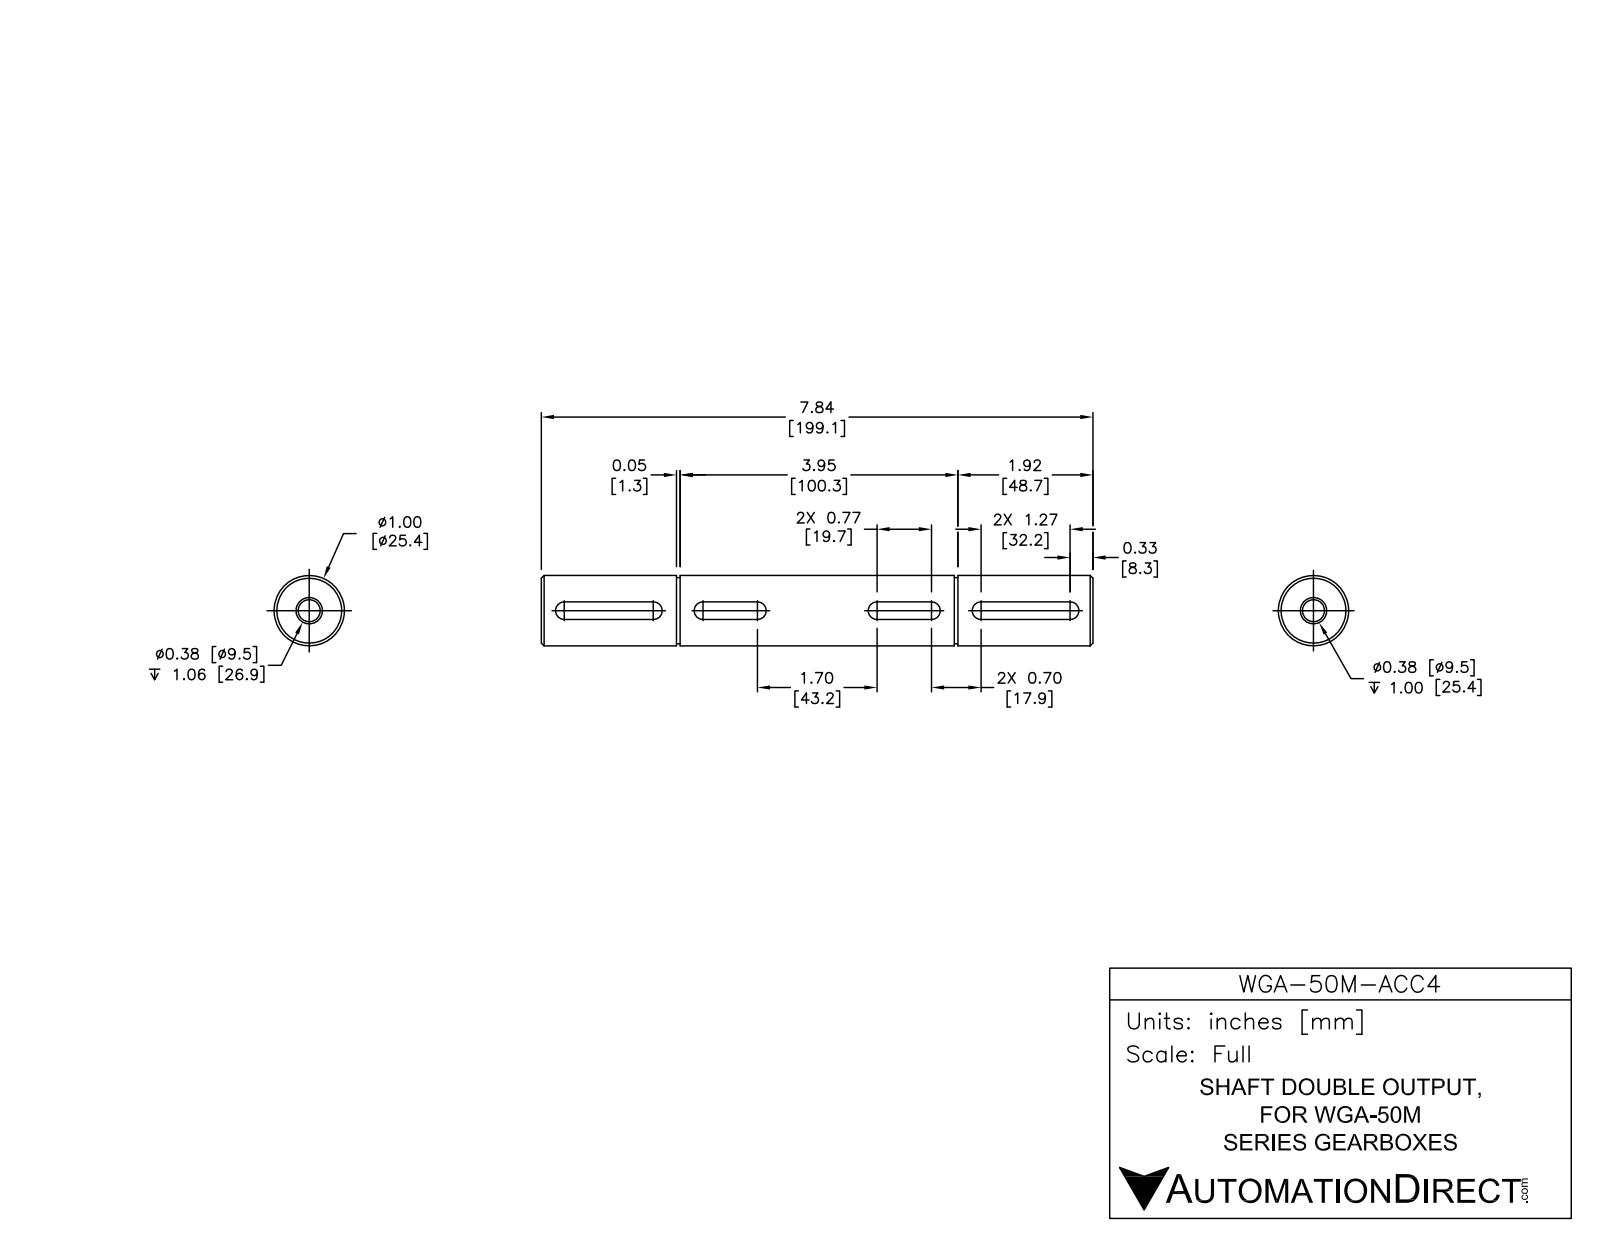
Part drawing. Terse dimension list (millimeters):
name: WGA-50M-ACC4
written by: SolidWorks 2014 (AUTOMOTIVE_DESIGN)
unit: mm
bodies: 1 solid, 54 faces (20 planar, 26 cylindrical, 8 other)
size: 199.1 × 25.4 × 25.4
volume: 94 390 mm³; area: 19 500 mm²
holes: 1× ⌀8, 1× ⌀9.5, 1× ⌀9.5
bosses: 1× ⌀25.4, 1× ⌀23.9
rounds: 8× R3.2
face distances: 199.1, 6.4, 6.4, 1.3, 100.3, 6.4, 150.4, 48.7, 149.1, 50
